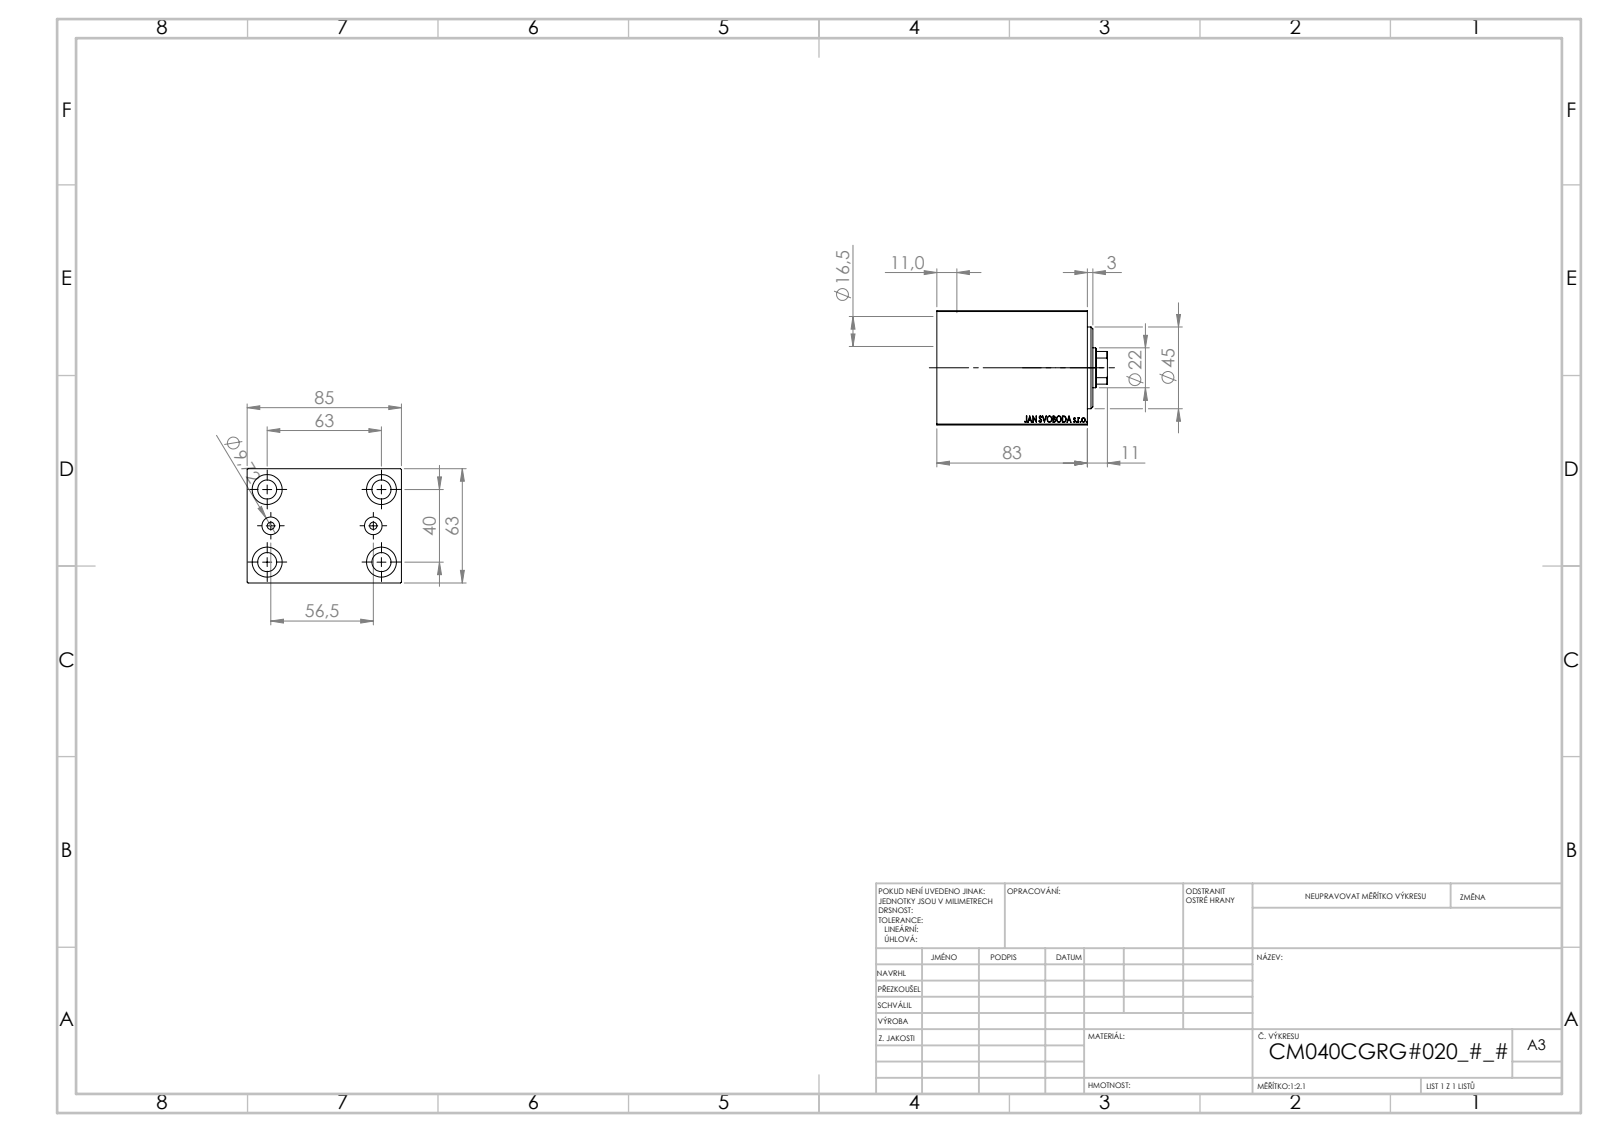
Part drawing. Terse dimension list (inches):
name: V450CM_C_VCP; V450CM_C_Body; V450CM_VC_B
written by: SolidWorks 2019 (CONFIG_CONTROL_DESIGN)
unit: in
bodies: 3 solids, 858 faces (408 planar, 56 cylindrical, 394 other)
size: 3.701 × 3.346 × 2.48
volume: 24.23 in³; area: 111.7 in²
holes: 4× ⌀0.413, 4× ⌀0.65, 2× ⌀0.157, 2× ⌀0.383, 1× ⌀0.492, 1× ⌀0.866, 1× ⌀1.004, 1× ⌀1.575, 1× ⌀1.654, 1× ⌀1.772
rounds: 1× R0.413
face distances: 2.48, 3.346, 3.268, 1.26, 2.008, 0.433, 0.85, 1.157, 2.417, 0.394
hole spacings: 1.469, 0.791, 0.807, 1.575, 2.434, 2.48, 2.528, 2.938
